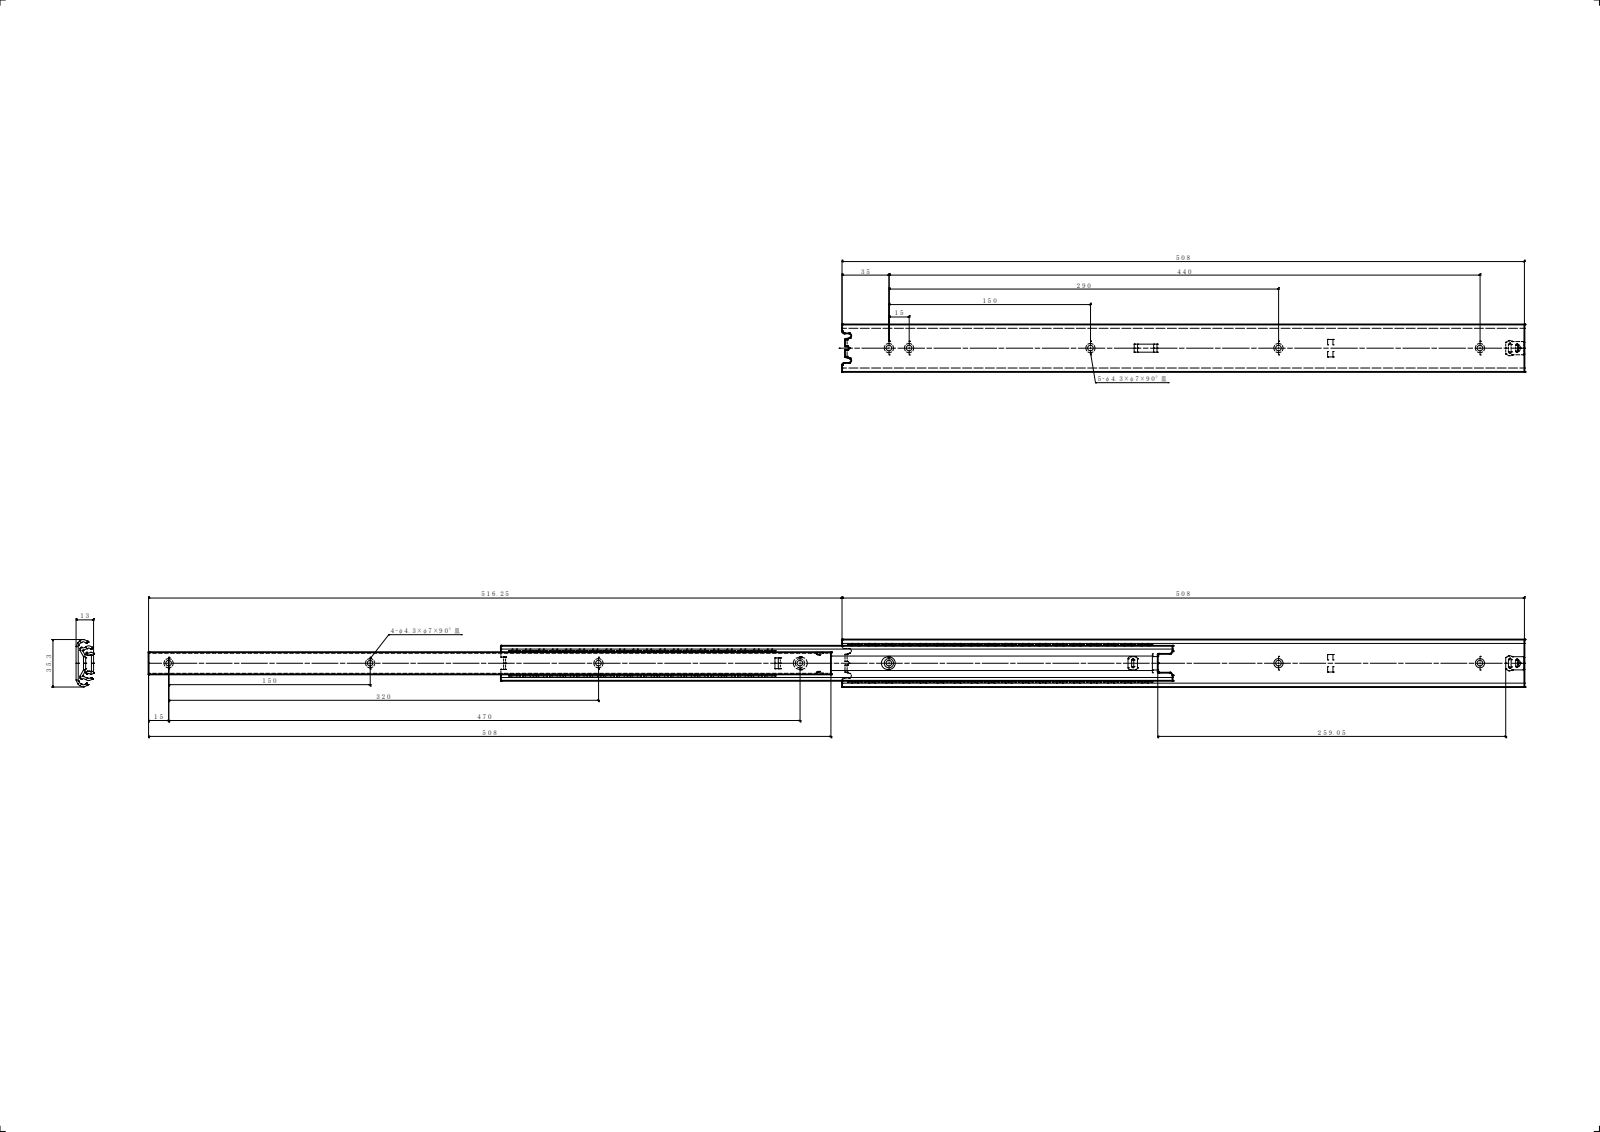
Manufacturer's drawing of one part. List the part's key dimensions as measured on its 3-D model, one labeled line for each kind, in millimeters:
Part name (STEP PRODUCT): C351-20 CM; C351-20 OM; PN32; C351-20 IM (+2 more)
STEP written by: SolidWorks 2019 (CONFIG_CONTROL_DESIGN)
Units: millimetres
Bodies: 5 solids, 294 faces (146 planar, 128 cylindrical, 20 other)
Overall size (bounding box): 1024.29 × 35.3 × 13
Volume: 89 043 mm³ · Surface area: 115 464 mm²
Round holes (diameter × count): ⌀4.3 ×9, ⌀4.5 ×1
Partial cylindrical surfaces — rounded edges, fillets, slot ends (radius × count): R0.5 ×21, R1.5 ×8, R0.3 ×6, R0.8 ×4, R1 ×4, R1.6 ×4, R2 ×4, R2.38 ×4
Main face-to-face distances: 1.6, 11.4, 5.4, 6, 13, 9.8, 3.8, 7.6, 7, 4.4
Hole centre spacings: 150, 216.29, 290, 320, 506.29, 536.29, 826.29, 15
